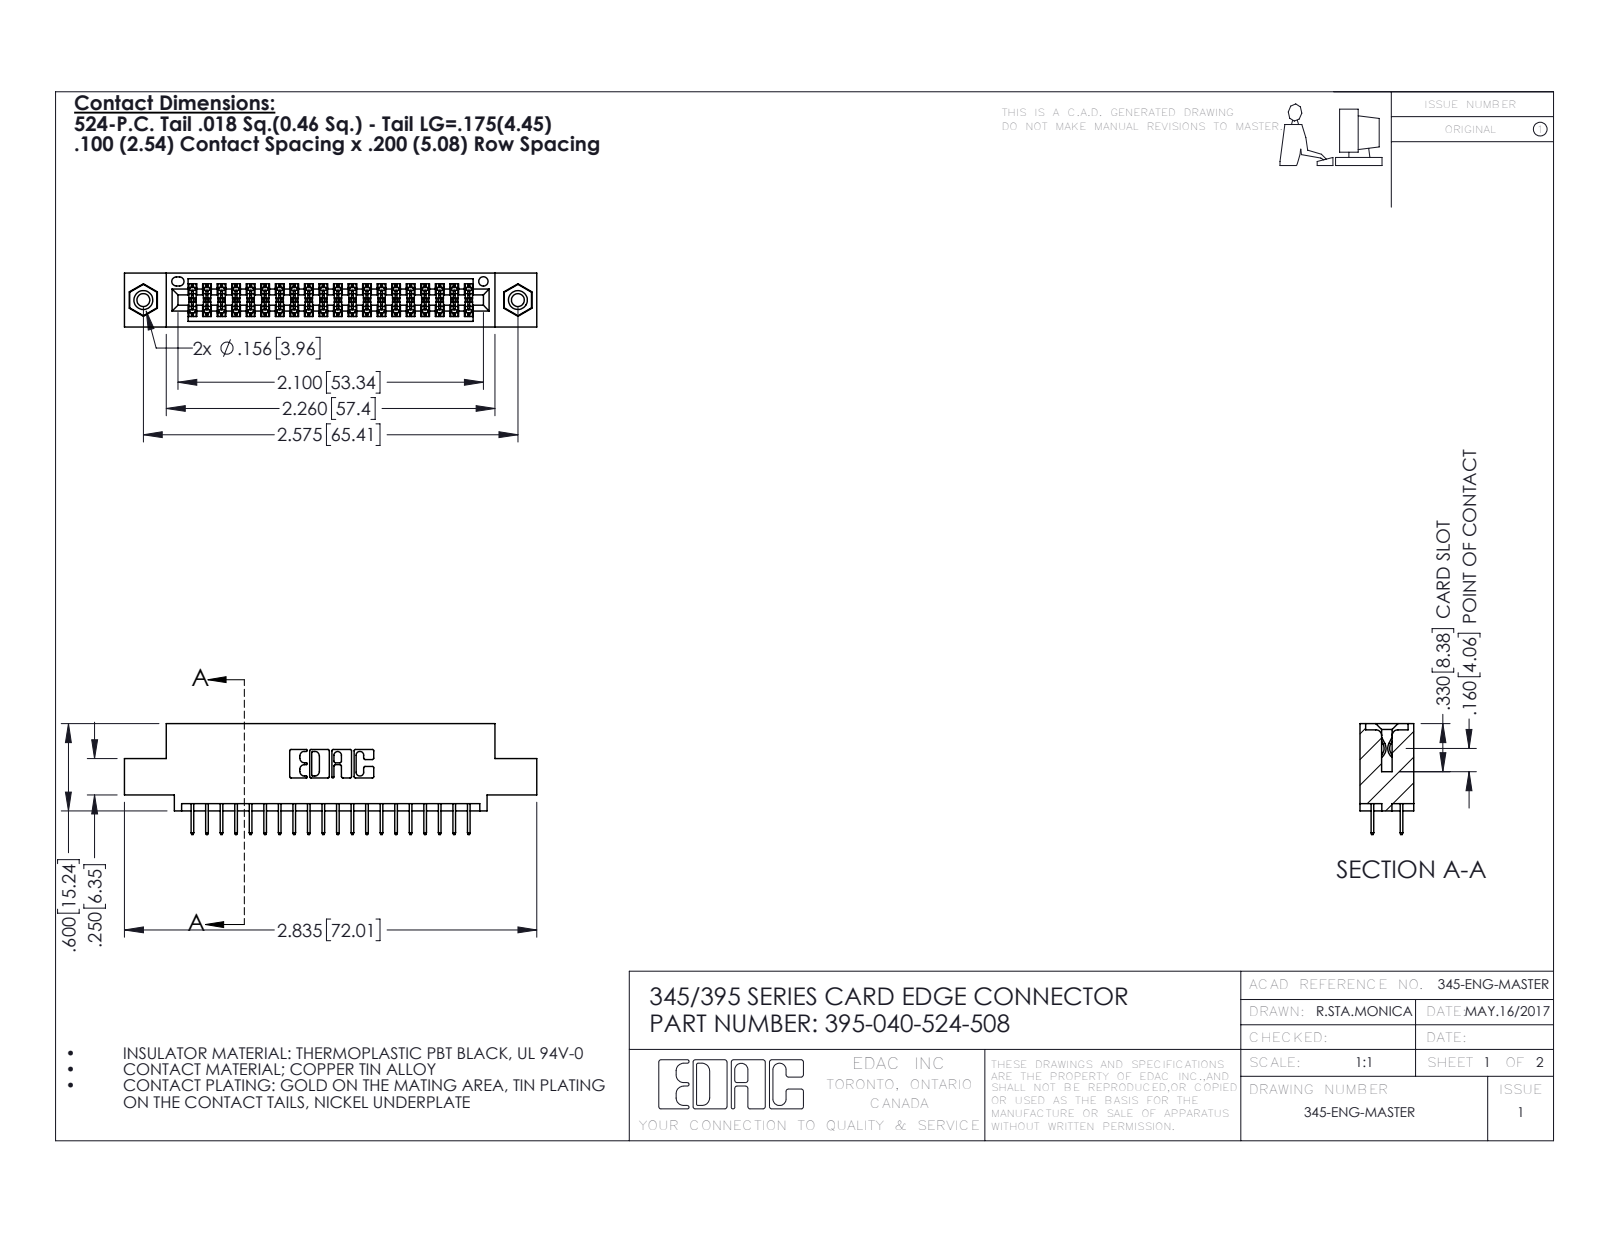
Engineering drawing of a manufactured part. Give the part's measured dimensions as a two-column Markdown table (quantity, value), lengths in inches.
| quantity | value |
| --- | --- |
| part name | 345-250-001_345-250-003-102; 395-040-524-508; 345 Part_0.110 Offset - 0.156 Dia-TI; 345-292-001_345-293-124 |
| STEP written by | SolidWorks 2016 (CONFIG_CONTROL_DESIGN) |
| units | inches |
| bodies | 43 solids, 2350 faces (1676 planar, 658 cylindrical, 16 other) |
| overall size | 2.835 × 0.762 × 0.37 |
| volume | 0.406 in³ |
| surface area | 14.49 in² |
| round holes (diameter × count) | 0.089 × 2, 0.125 × 2, 0.156 × 2, 0.064 × 1 |
| round bosses / shafts (diameter × count) | 0.155 × 2 |
| partial cylindrical surfaces (radius × count) | 0.006 × 60, 0.01 × 22, 0.007 × 6, 0.031 × 6, 0.026 × 3, 0.014 × 2, 0.019 × 2, 0.022 × 2 |
| main face-to-face distances | 0.072, 0.298, 0.2, 0.37, 0.098, 0.272, 0.025, 0.225, 0.072, 0.175 |
| hole center spacings | 0.27, 2.341, 2.575 |
